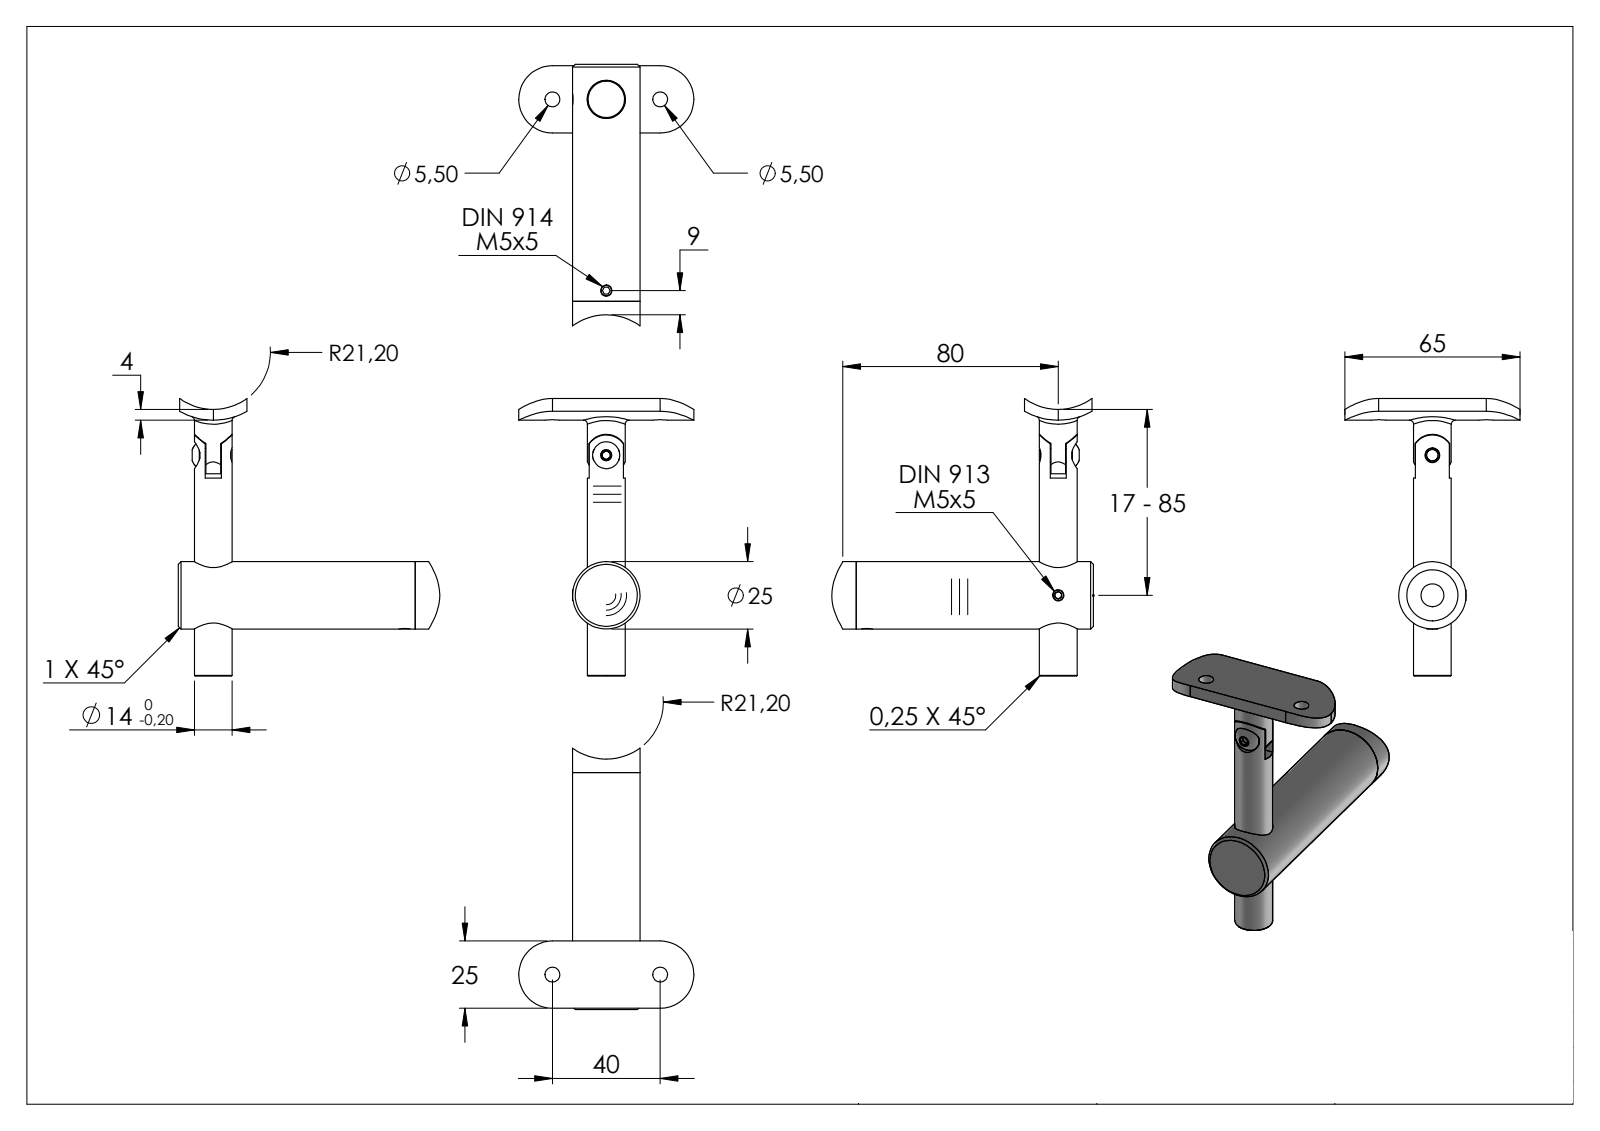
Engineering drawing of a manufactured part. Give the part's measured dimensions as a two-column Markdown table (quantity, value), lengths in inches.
| quantity | value |
| --- | --- |
| part name | DIN914; 5037X-240 Teil2_50374-240 Teil2; DIN913; 5037X-240 Teil1 (+8 more) |
| STEP written by | SolidWorks 2018 (CONFIG_CONTROL_DESIGN) |
| units | inches |
| bodies | 7 solids, 370 faces (153 planar, 82 cylindrical, 135 other) |
| overall size | 4.058 × 3.822 × 3.465 |
| volume | 3.623 in³ |
| surface area | 34.45 in² |
| round holes (diameter × count) | 0.165 × 3, 0.217 × 3, 0.335 × 1, 0.394 × 1, 0.559 × 1, 0.63 × 1, 0.748 × 1 |
| round bosses / shafts (diameter × count) | 0.197 × 3, 0.984 × 1, 0.551 × 1 |
| partial cylindrical surfaces (radius × count) | 0.305 × 3, 0.492 × 2, 0.835 × 2, 0.319 × 1, 0.992 × 1 |
| main face-to-face distances | 3.465, 0.374, 0.61, 0.384, 0.226, 0.6, 0.118, 3.583, 3.563, 3.445 |
| hole center spacings | 0.787, 2.904, 1.575, 2.047, 2.795 |
